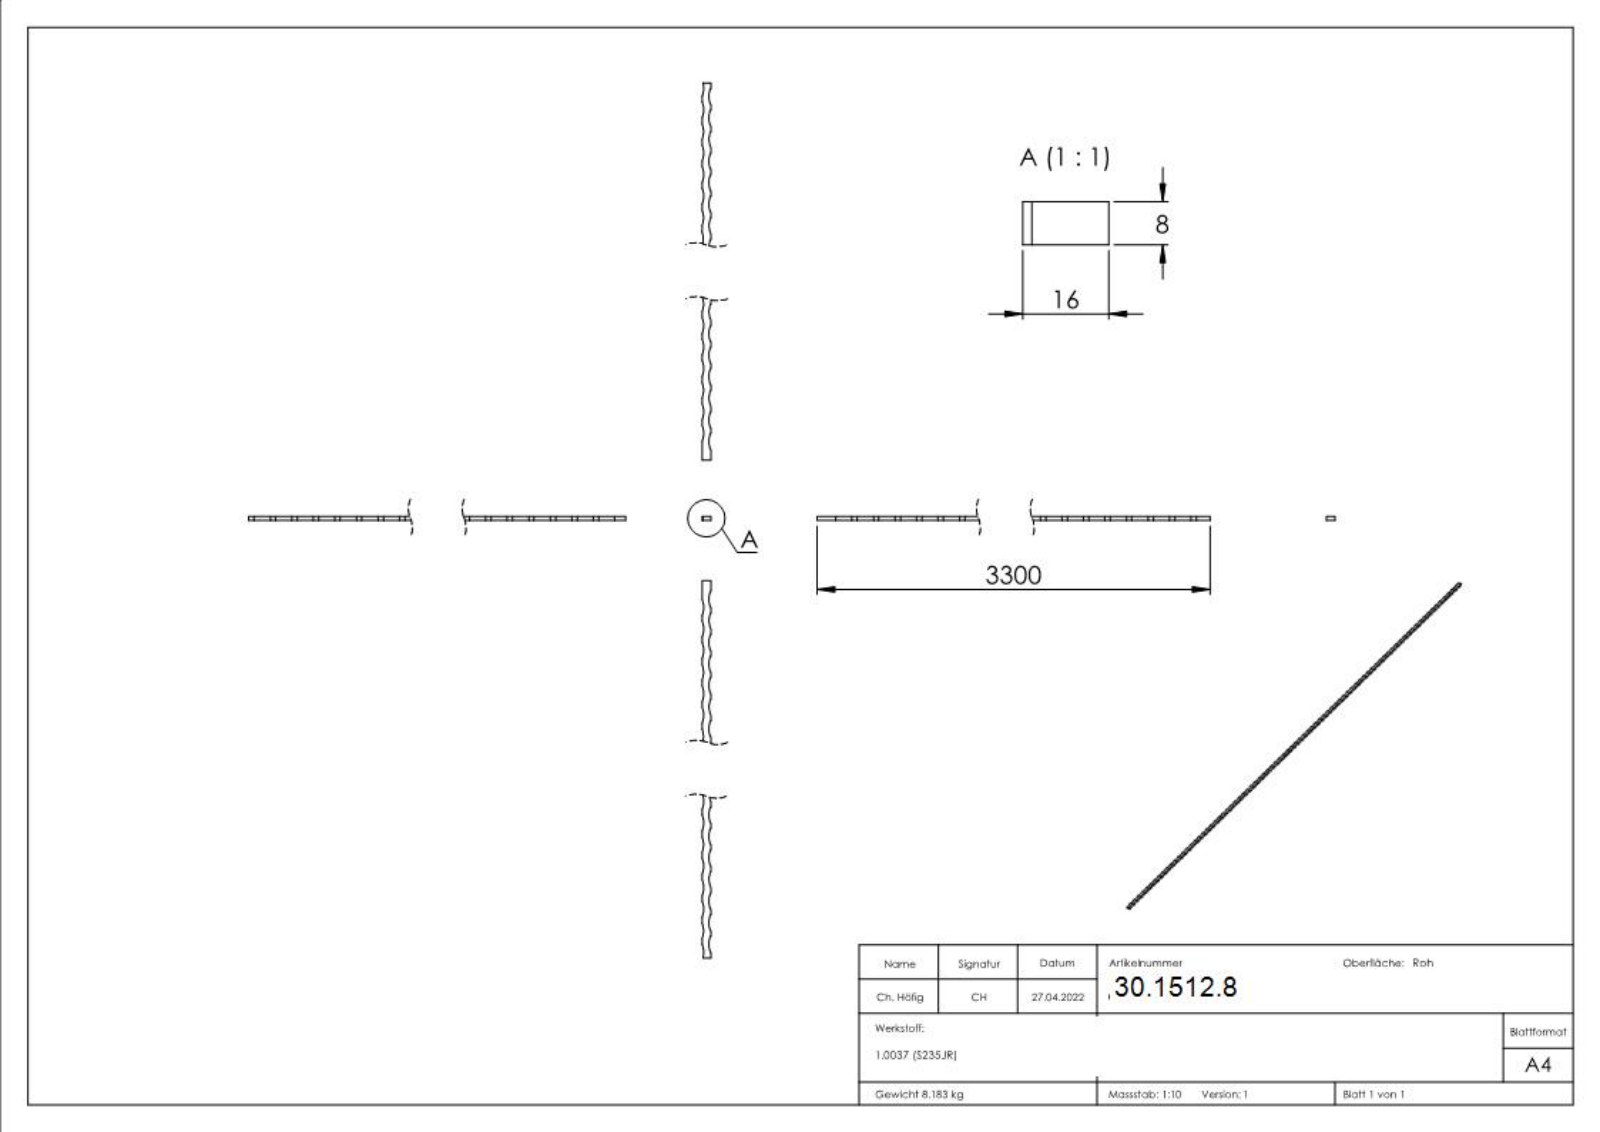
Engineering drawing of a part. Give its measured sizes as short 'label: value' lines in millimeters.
name: 6008
written by: SolidWorks 2018 (CONFIG_CONTROL_DESIGN)
unit: mm
bodies: 1 solid, 545 faces (269 planar, 164 cylindrical, 112 other)
size: 3300 × 16 × 8
volume: 343 089 mm³; area: 139 864 mm²
rounds: 164× R39
face distances: 8, 16, 3300, 7.9, 0.34, 1650, 6.99, 9.01, 0.32, 1.37
